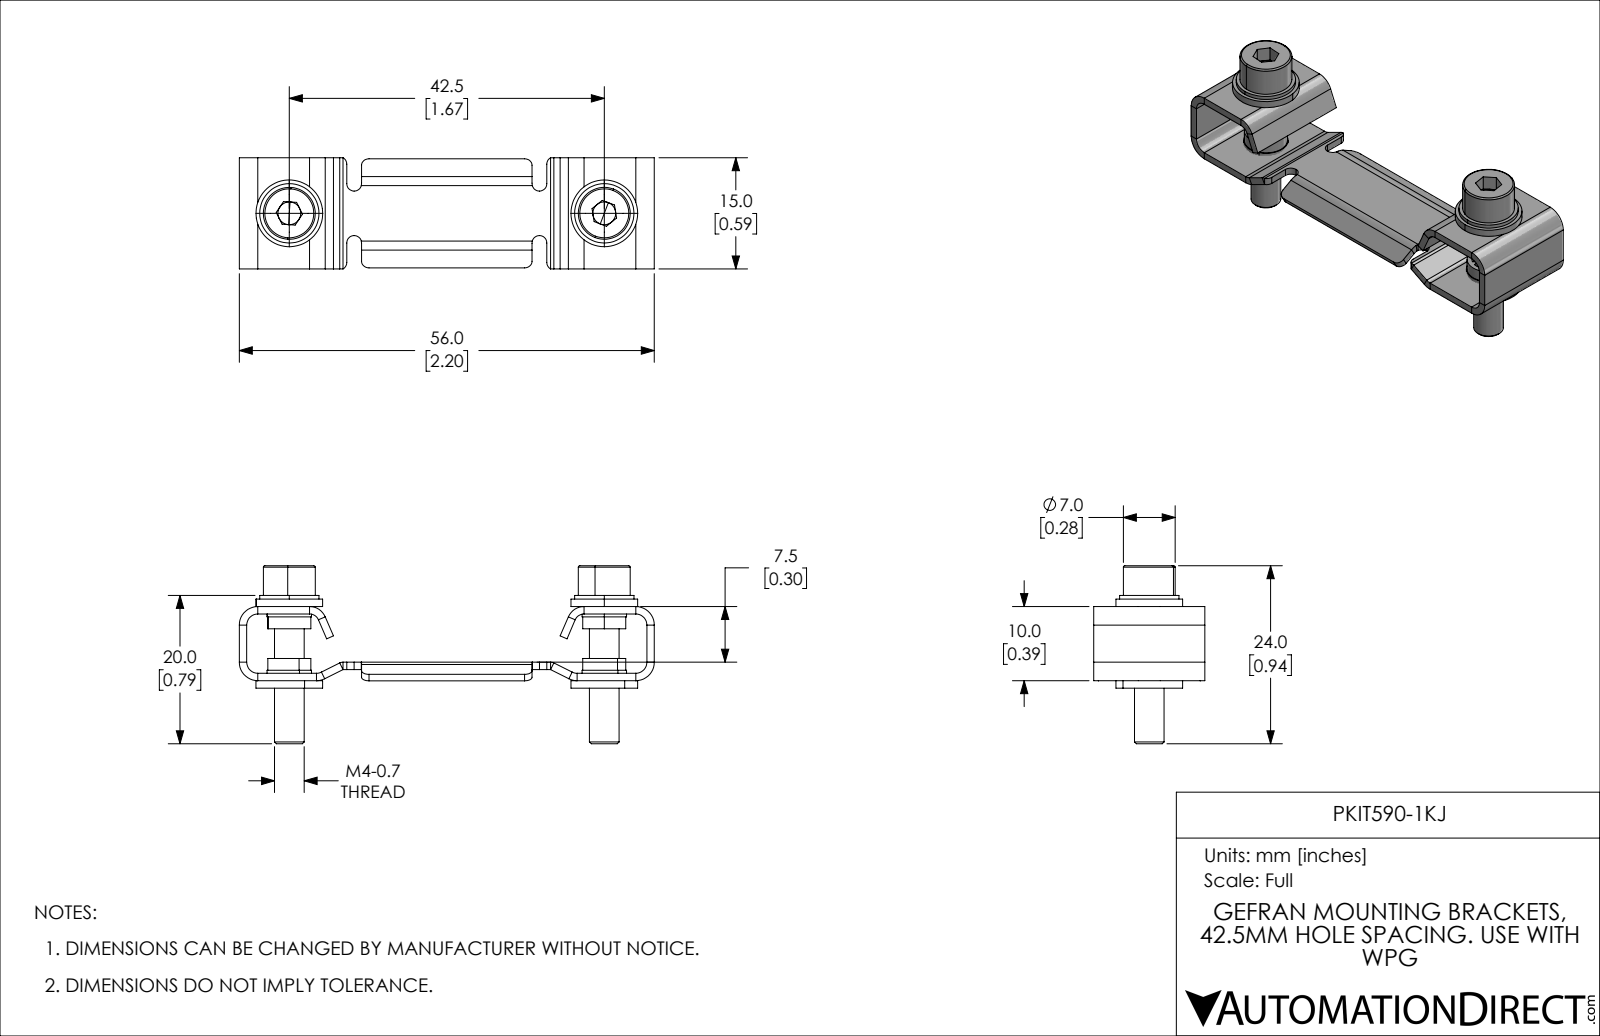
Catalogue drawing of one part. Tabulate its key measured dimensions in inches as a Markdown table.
| quantity | value |
| --- | --- |
| part name | PKIT590-1KJ |
| STEP written by | SolidWorks 2021 (CONFIG_CONTROL_DESIGN) |
| units | inches |
| bodies | 9 solids, 335 faces (176 planar, 109 cylindrical, 50 other) |
| overall size | 2.205 × 0.945 × 0.591 |
| volume | 0.151 in³ |
| surface area | 7.738 in² |
| round holes (diameter × count) | 0.169 × 2, 0.177 × 2, 0.232 × 2 |
| round bosses / shafts (diameter × count) | 0.354 × 2, 0.315 × 2, 0.276 × 2, 0.236 × 2, 0.228 × 2, 0.157 × 2 |
| partial cylindrical surfaces (radius × count) | 0.039 × 14, 0.014 × 12, 0.059 × 8, 0.098 × 8, 0.051 × 2, 0.091 × 2 |
| main face-to-face distances | 0.039, 0.394, 0.059, 0.354, 0.335, 0.098, 0.295, 0.02, 0.079, 0.433 |
| hole center spacings | 1.673 |
